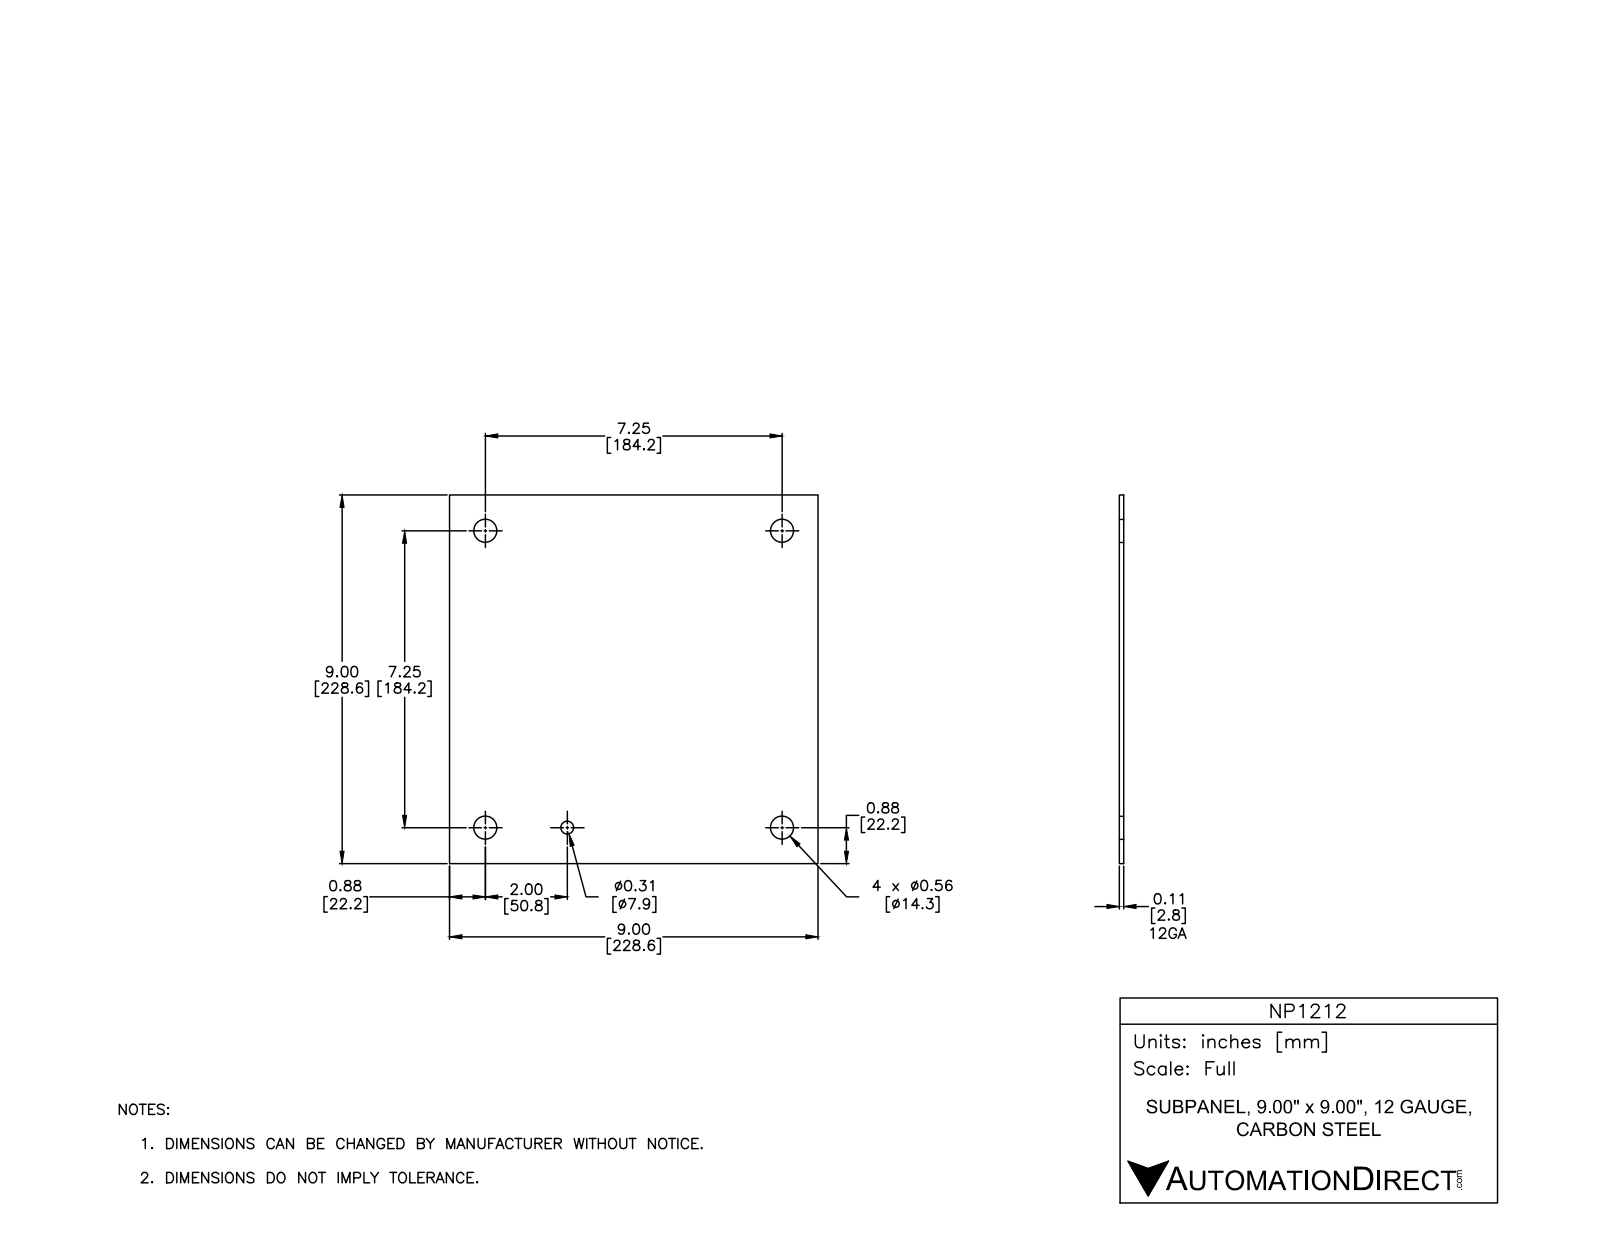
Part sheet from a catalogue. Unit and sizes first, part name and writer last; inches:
Units: inches
Overall size (bounding box): 9 × 9 × 0.094
Round holes (diameter × count): ⌀0.563 ×4, ⌀0.31 ×1
Main face-to-face distances: 0.094, 9
Hole centre spacings: 7.25, 2, 5.25, 7.25, 7.521, 8.951, 10.253, 10.254
Volume: 7.493 in³ · Surface area: 164 in²
Bodies: 1 solid, 11 faces (6 planar, 5 cylindrical, 0 other)
Part name (STEP PRODUCT): NP1212
STEP written by: Autodesk Inventor 2012 (AUTOMOTIVE_DESIGN)
